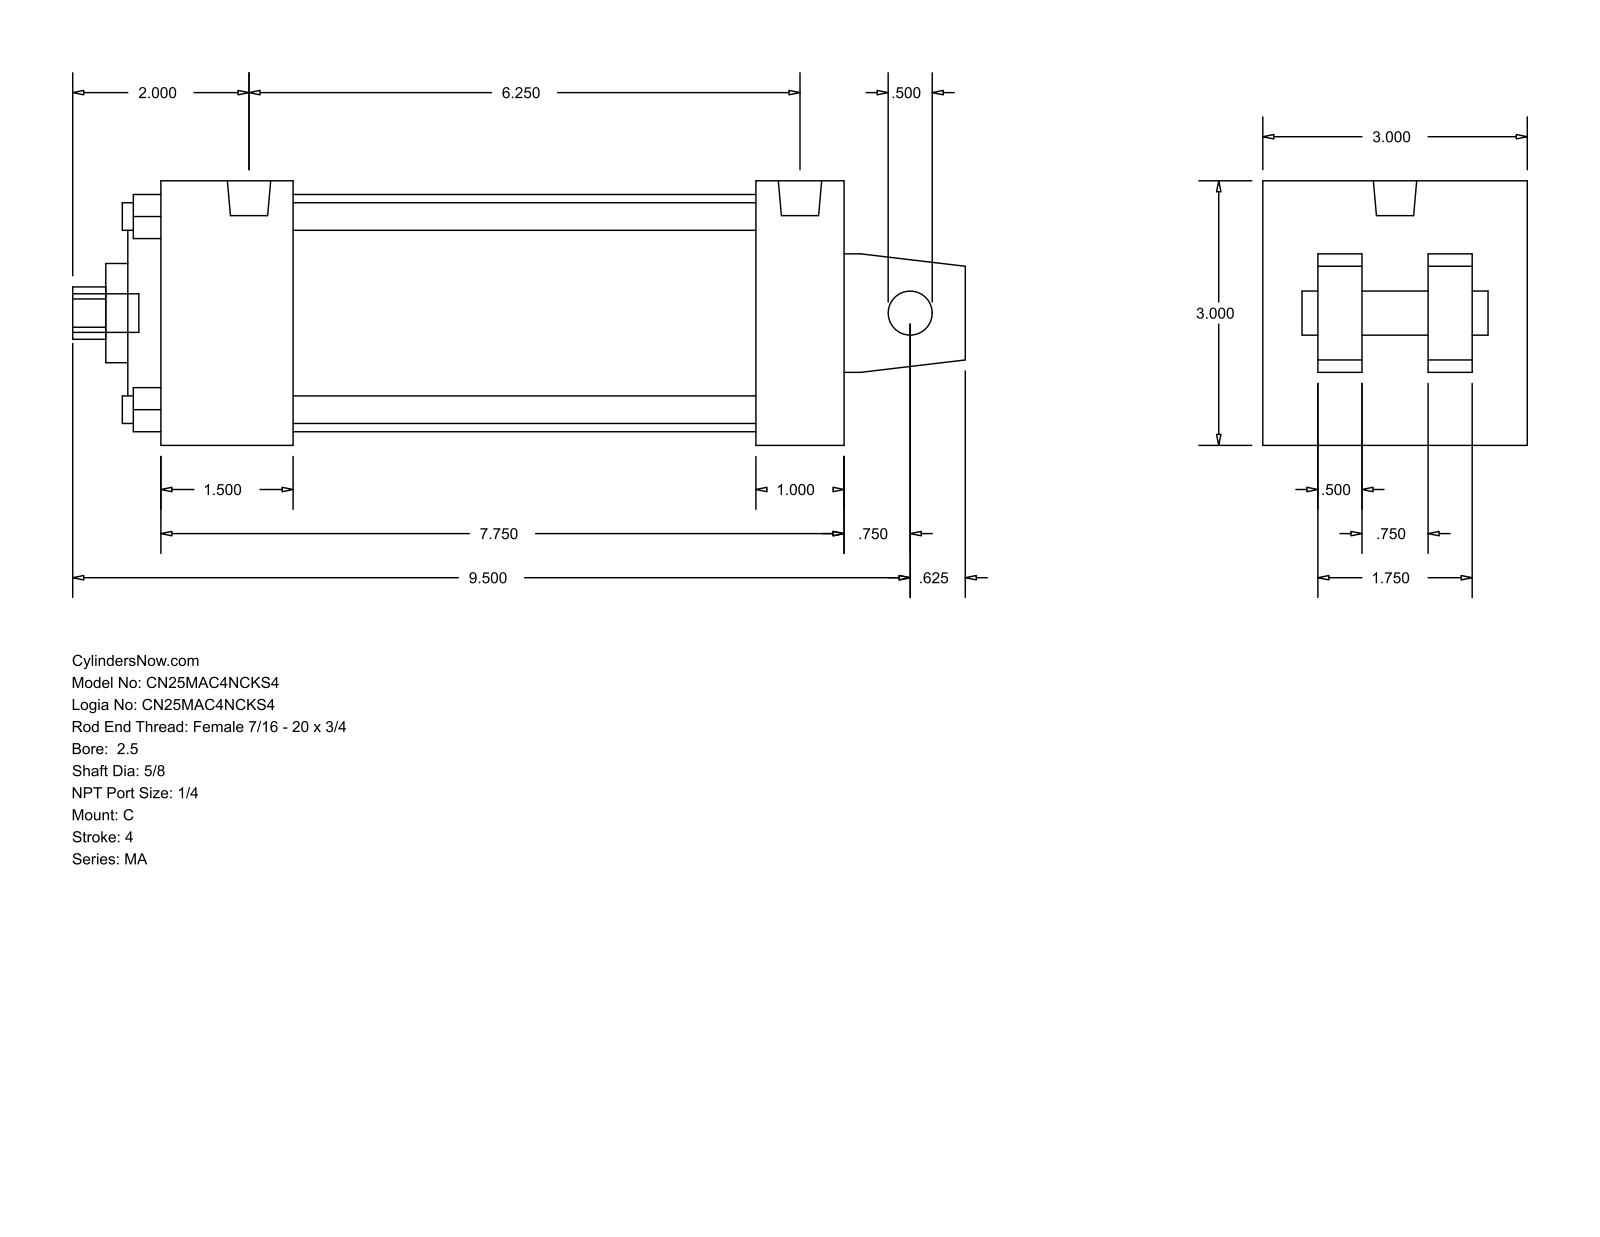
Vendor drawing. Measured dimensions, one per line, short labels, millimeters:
name: MA_C__0250_0.625
written by: GSSL Pune (CONFIG_CONTROL_DESIGN)
unit: mm
bodies: 0 solids, 105 faces (77 planar, 28 cylindrical, 0 other)
size: 257.18 × 76.2 × 76.2
holes: 4× ⌀7.94, 1× ⌀12.7, 1× ⌀15.88, 1× ⌀28.57, 1× ⌀50.8, 1× ⌀68.33
bosses: 4× ⌀7.94, 2× ⌀12.49, 1× ⌀11.11
rounds: 1× R7.54
face distances: 76.2, 196.85, 12.7, 15.87, 60.33, 47.63, 25.4, 38.1, 171.45, 133.35
hole spacings: 39.33, 55.62, 78.66
